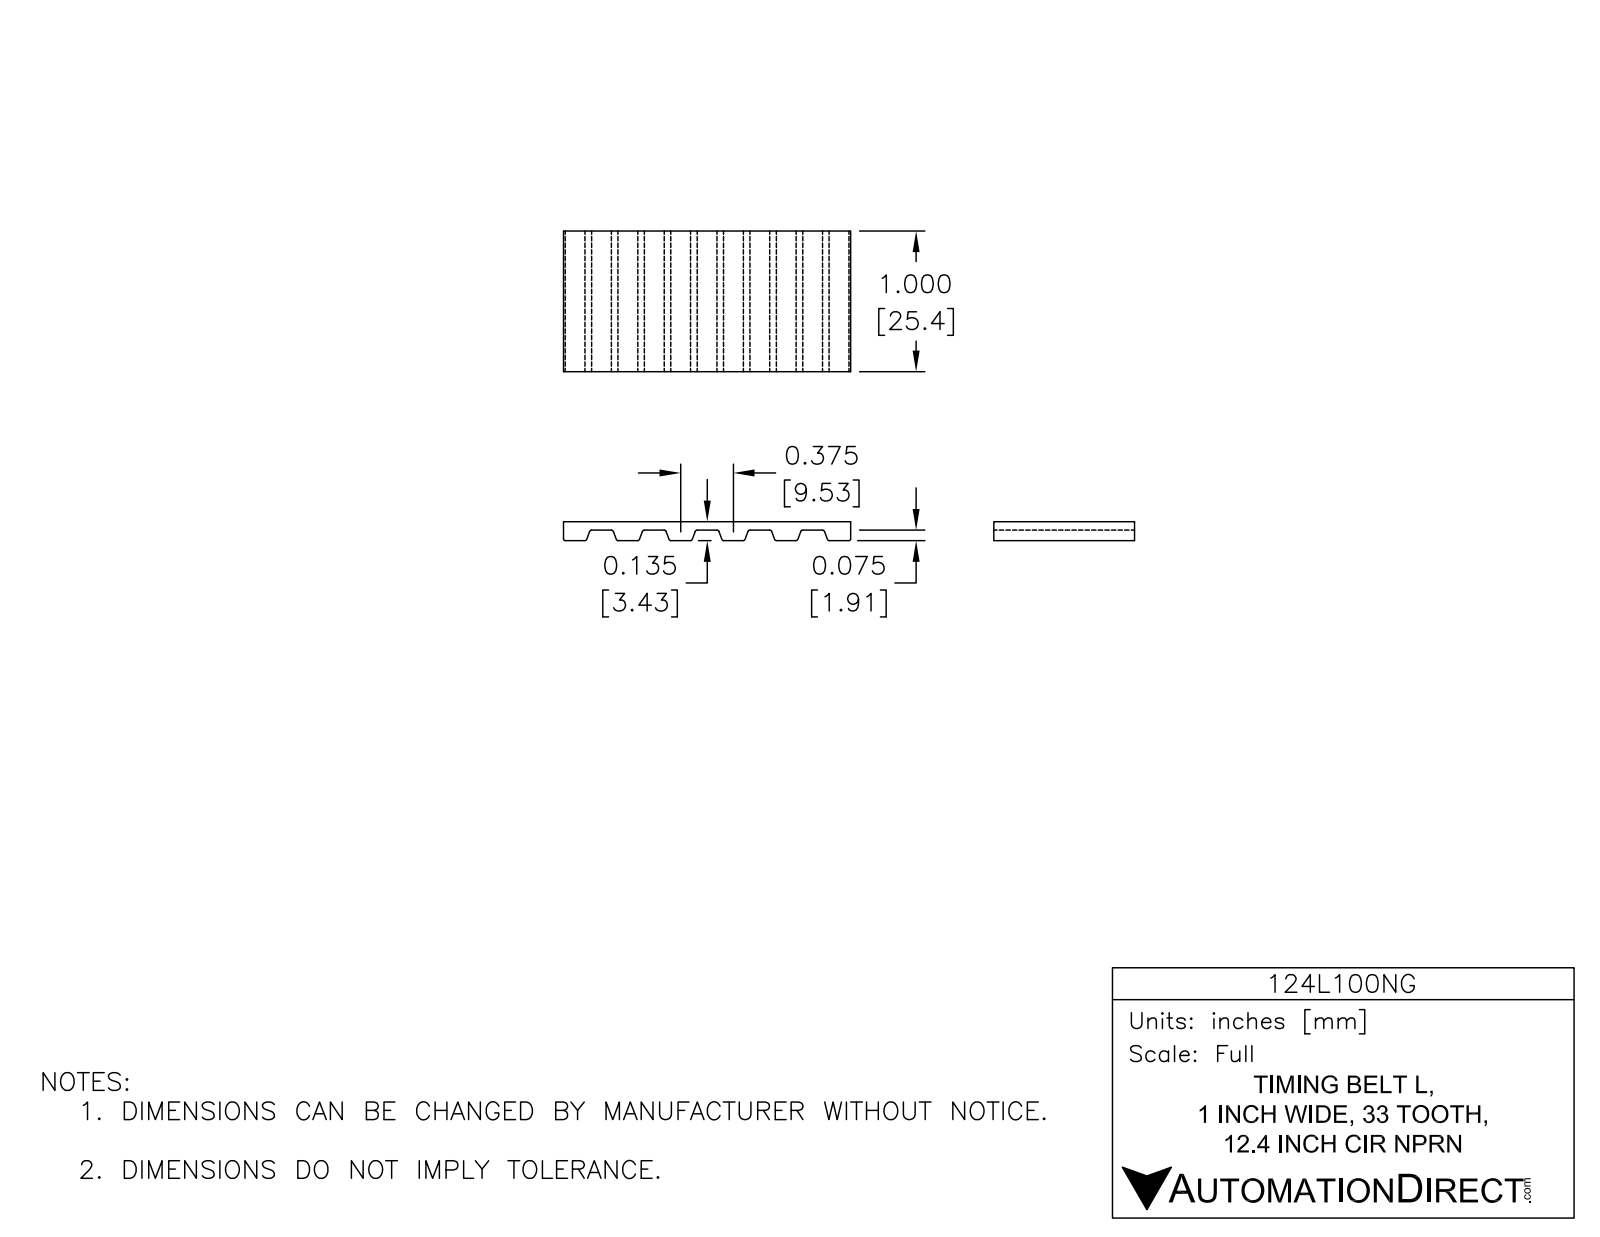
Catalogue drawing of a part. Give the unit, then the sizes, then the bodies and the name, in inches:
Units: inches
Overall size (bounding box): 4.475 × 3 × 1
Partial cylindrical surfaces — rounded edges, fillets, slot ends (radius × count): R0.02 ×128, R1.435 ×2, R1.5 ×2
Main face-to-face distances: 0.065, 2.935, 3, 1, 2.87, 0.14, 2.86, 0.075, 2.795, 0.352
Volume: 1.102 in³ · Surface area: 29.43 in²
Bodies: 1 solid, 279 faces (108 planar, 171 cylindrical, 0 other)
Part name (STEP PRODUCT): 124L100NG
STEP written by: SolidWorks 2014 (AUTOMOTIVE_DESIGN)
